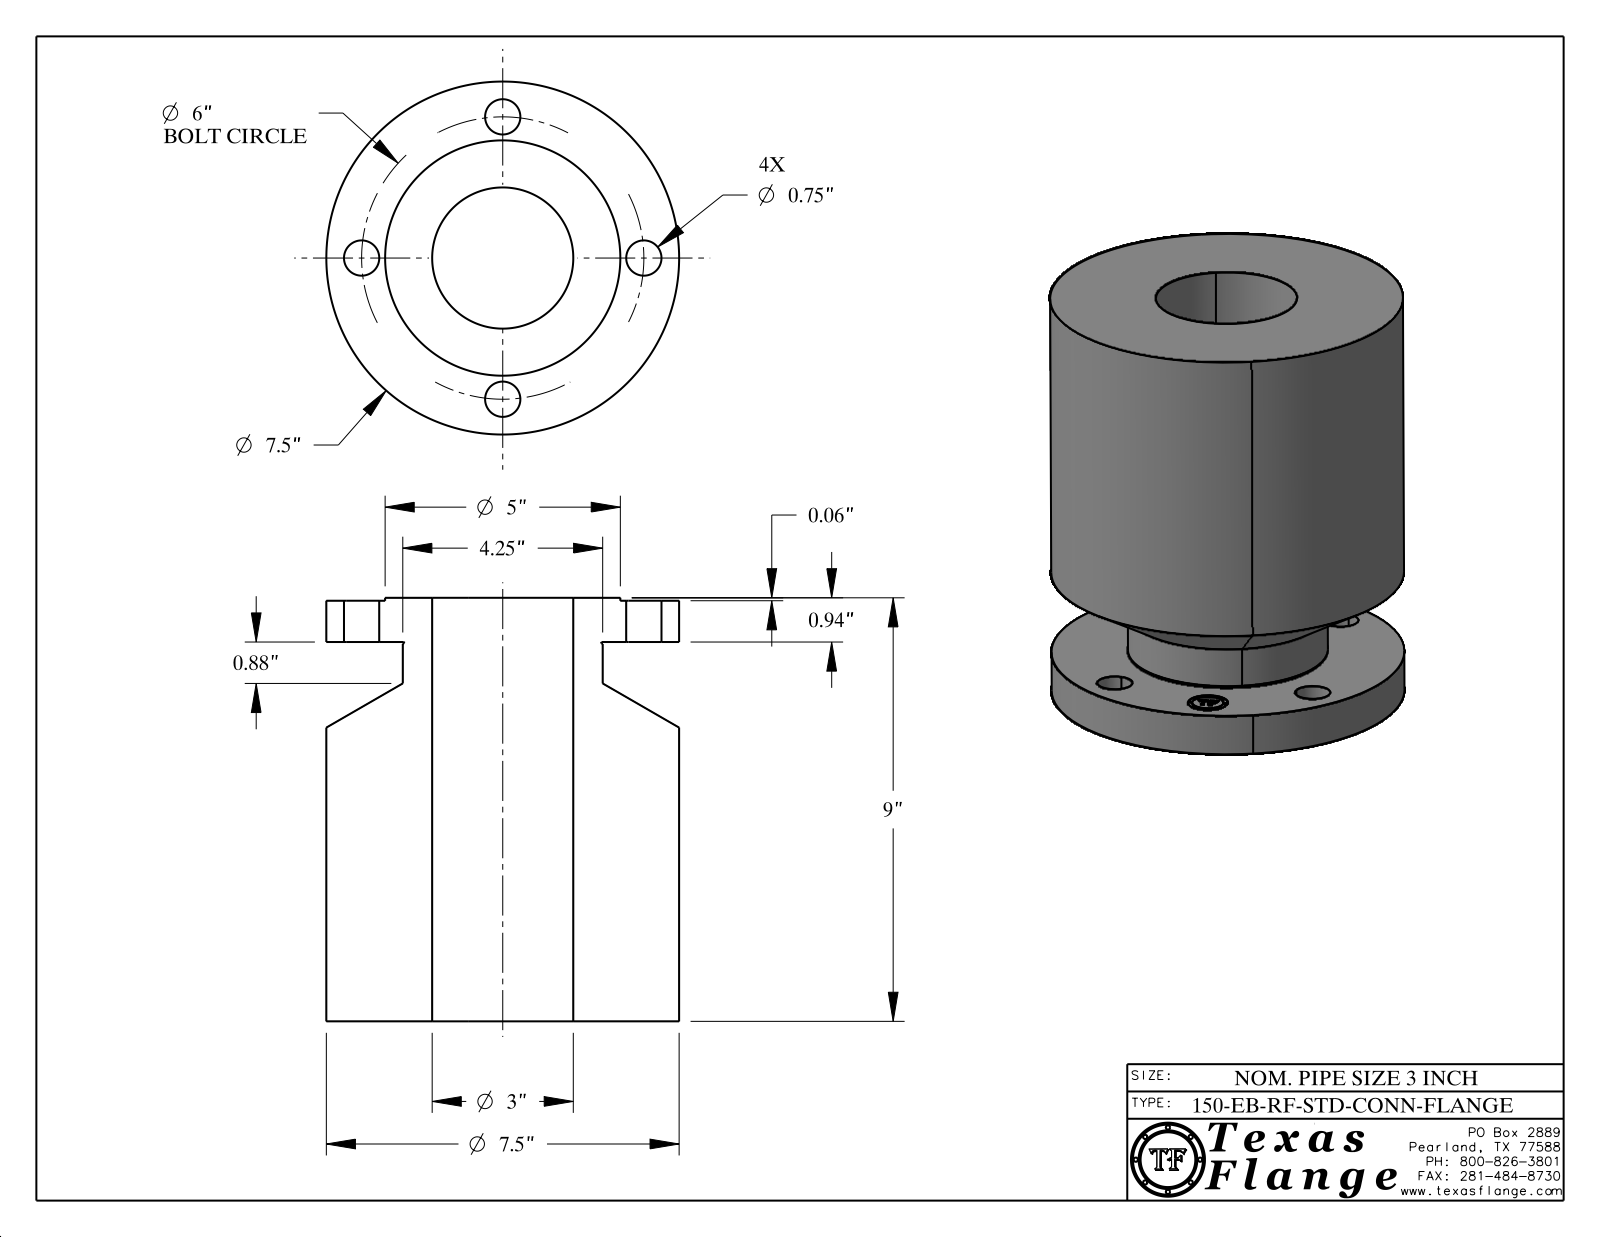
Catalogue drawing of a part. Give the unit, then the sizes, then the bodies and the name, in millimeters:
Units: millimetres
Overall size (bounding box): 228.6 × 190.5 × 190.5
Round holes (diameter × count): ⌀19.1 ×4, ⌀21.6 ×1, ⌀76.2 ×1
Round bosses / shafts (diameter × count): ⌀1.3 ×8, ⌀190.5 ×1, ⌀127 ×1, ⌀108 ×1, ⌀17 ×1
Main face-to-face distances: 204.7, 22.3, 227, 1.6, 23.9, 228.6, 23.7, 22.1, 204.9, 6.5
Hole centre spacings: 76.2, 107.8, 58.3, 140.8, 152.4
Volume: 4 738 000 mm³ · Surface area: 264 100 mm²
Bodies: 1 solid, 413 faces (369 planar, 38 cylindrical, 6 other)
Part name (STEP PRODUCT): 3-150-EB-RF-STD-CONN-FLANGE
STEP written by: CATIA V5 STEP AP214 (AUTOMOTIVE_DESIGN)
